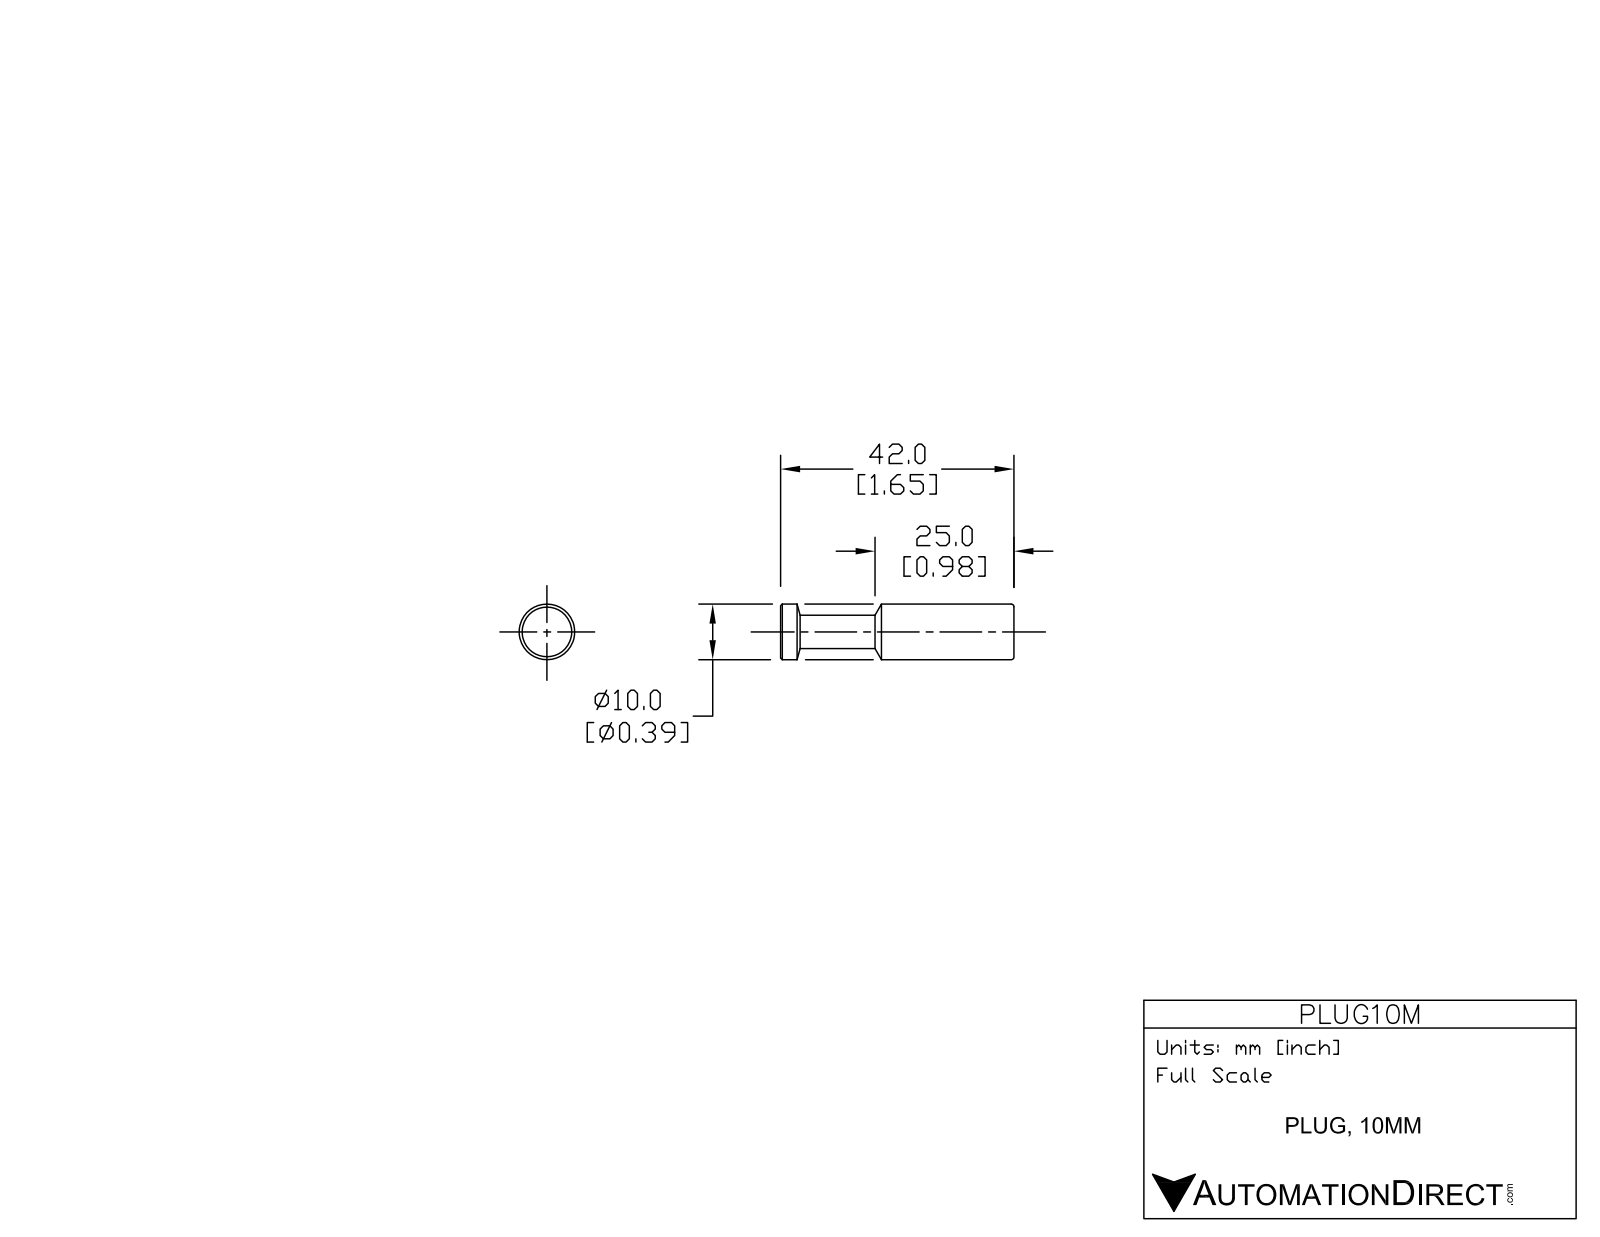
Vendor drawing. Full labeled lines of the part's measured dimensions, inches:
Part name (STEP PRODUCT): PLUG10M
STEP written by: SolidWorks 2015 (AUTOMOTIVE_DESIGN)
Units: inches
Bodies: 1 solid, 16 faces (2 planar, 6 cylindrical, 8 other)
Overall size (bounding box): 1.654 × 0.394 × 0.394
Volume: 0.157 in³ · Surface area: 2.095 in²
Round bosses / shafts (diameter × count): ⌀0.394 ×1, ⌀0.236 ×1
Main face-to-face distances: 1.654
